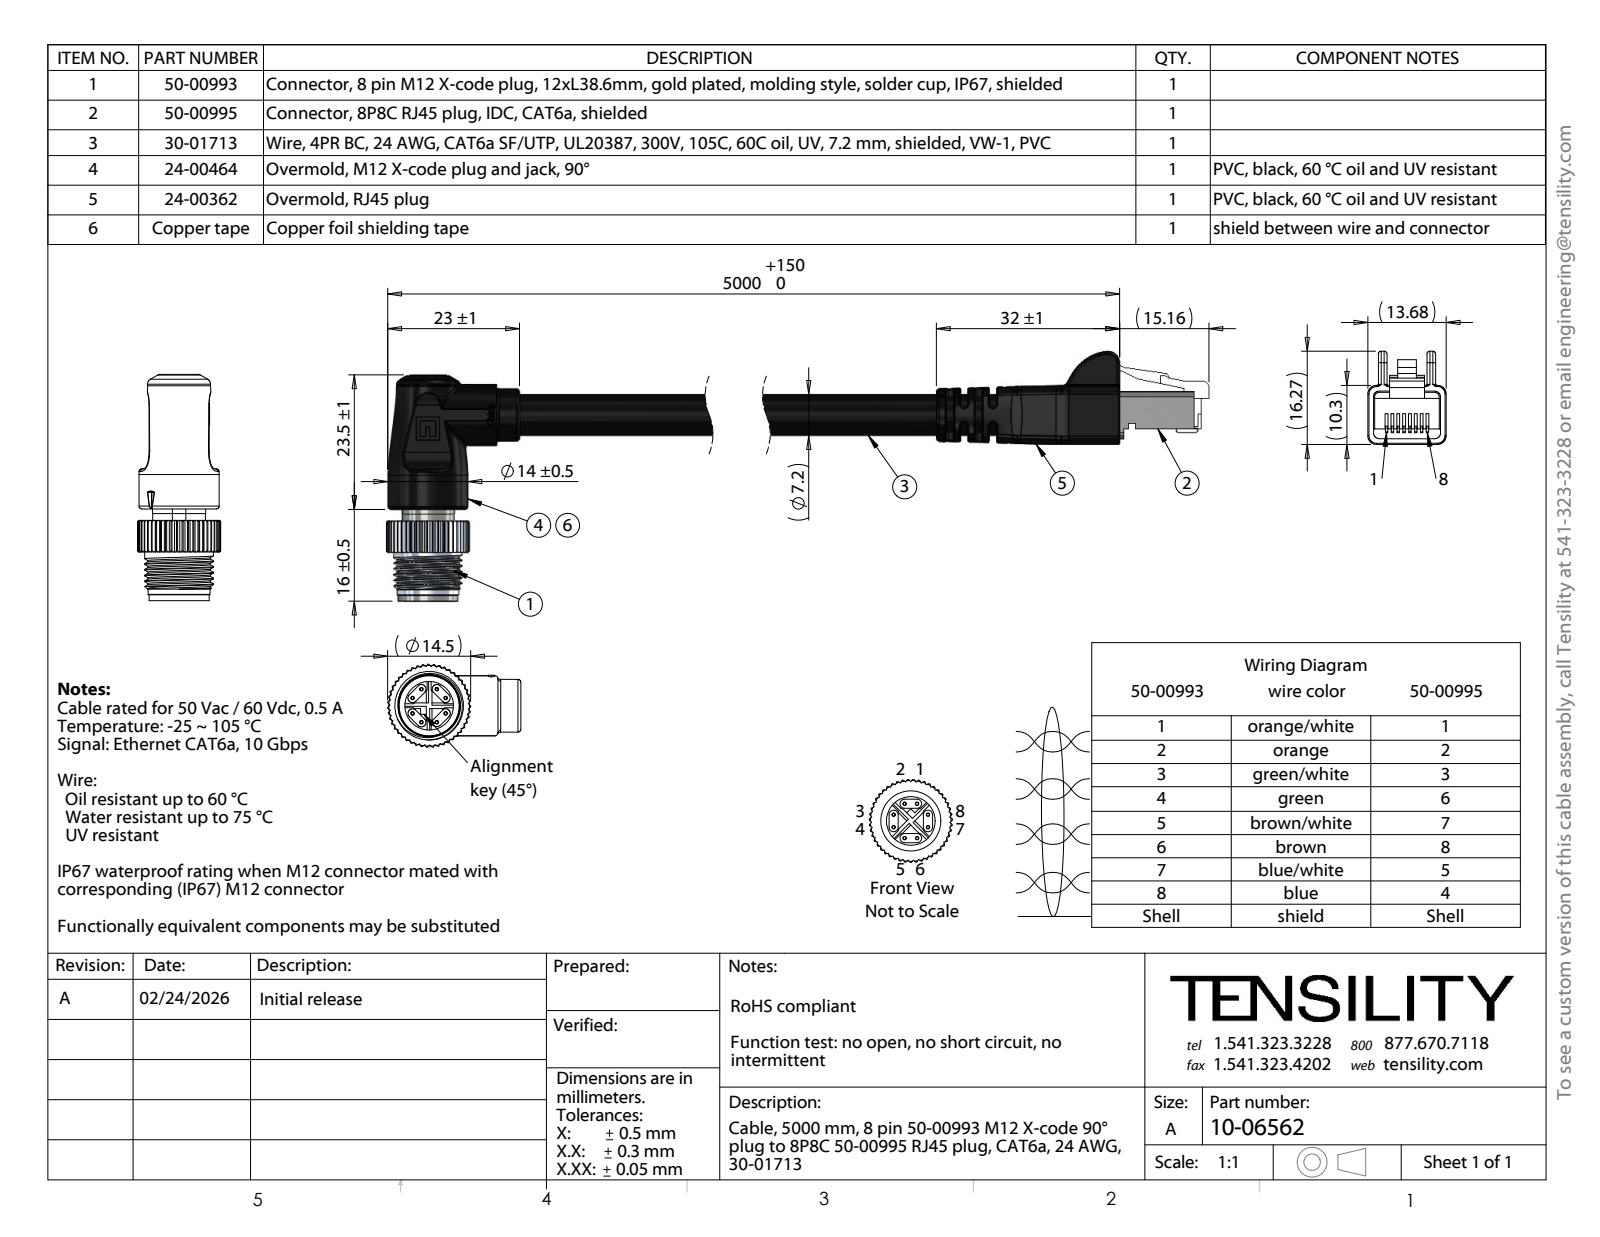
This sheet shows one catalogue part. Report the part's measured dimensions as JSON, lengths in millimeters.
{"part_name": "50-00993-03; 10-06562; 30-01713_blunt cut; 50-00995 (+7 more)", "step_written_by": "SolidWorks 2025 (CONFIG_CONTROL_DESIGN)", "units": "millimeters", "bodies": {"solids": 95, "faces": 2077, "planar": 843, "cylindrical": 677, "other": 557}, "overall_size": [210.35, 43.62, 14.49], "volume_mm3": 15667, "surface_area_mm2": 49597, "round_holes": [[0.2, 56], [0.6, 8], [1.2, 8], [2, 1], [2.5, 1], [5.03, 1], [5.25, 1], [5.65, 1], [5.75, 1], [7.5, 1], [8.5, 1], [9.07, 1]], "round_bosses_or_shafts": [[1.4, 8], [1.15, 8], [1.05, 8], [0.8, 8], [9.2, 2], [14, 1], [12, 1], [11, 1]], "partial_cylinders_radius": [[0.5, 14], [1, 13], [0.1, 12], [0.2, 11], [0.8, 10], [0.62, 8], [1.5, 8], [2.17, 4]], "face_to_face_distances": [0.5, 1, 0.99, 0.98, 2, 1.25, 5, 3.9, 3.75, 2.7], "hole_center_spacings": [0.35, 1.61, 1.78, 0.41, 1.06, 1.43, 1.93, 2.48]}
